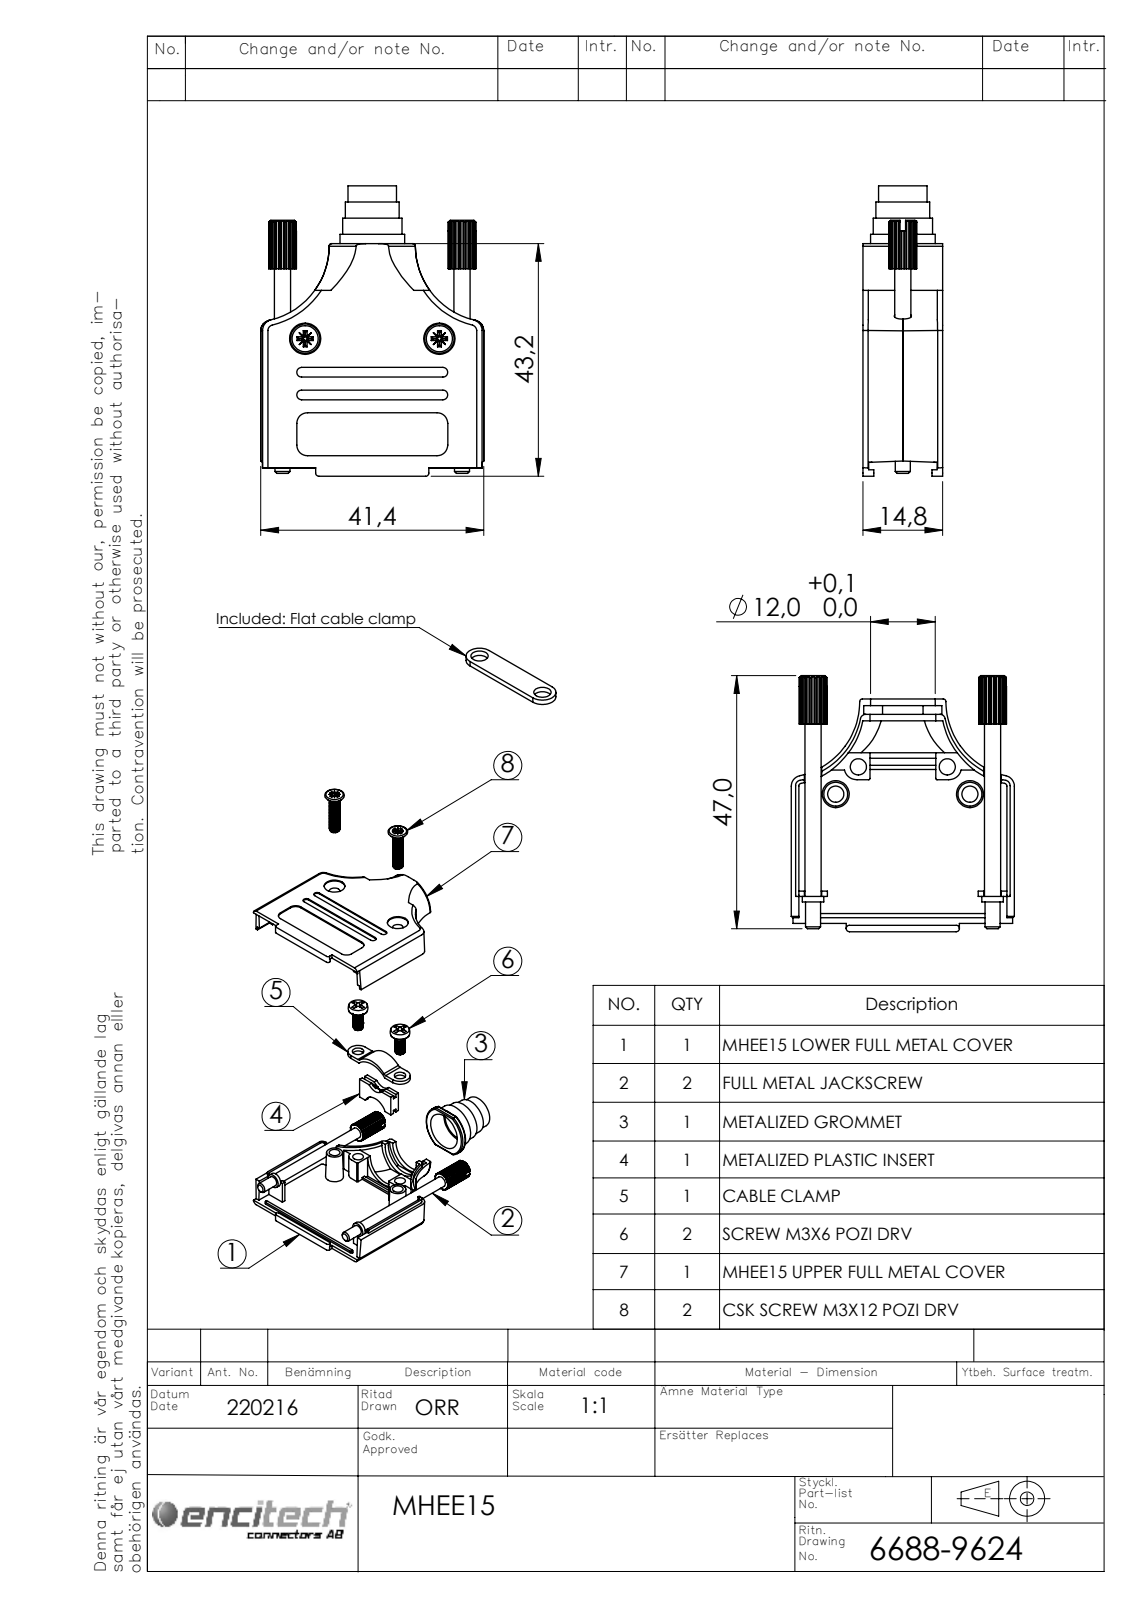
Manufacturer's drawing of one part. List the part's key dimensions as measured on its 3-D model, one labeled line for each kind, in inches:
Part name (STEP PRODUCT): 6560-0137-02; 6855-0117-13; 6826-0141-02; Cone MHEE (+5 more)
STEP written by: SolidWorks 2021 (AUTOMOTIVE_DESIGN)
Units: inches
Bodies: 11 solids, 877 faces (420 planar, 351 cylindrical, 106 other)
Overall size (bounding box): 2.122 × 1.63 × 0.583
Volume: 0.411 in³ · Surface area: 21.14 in²
Round holes (diameter × count): ⌀0.118 ×4, ⌀0.126 ×4, ⌀0.177 ×2, ⌀0.228 ×2, ⌀0.295 ×1, ⌀0.335 ×1, ⌀0.374 ×1, ⌀0.413 ×1, ⌀0.472 ×1, ⌀0.48 ×1
Round bosses / shafts (diameter × count): ⌀0.114 ×4, ⌀0.209 ×2, ⌀0.157 ×2, ⌀0.118 ×2, ⌀0.11 ×2, ⌀0.433 ×1, ⌀0.394 ×1, ⌀0.354 ×1
Partial cylindrical surfaces — rounded edges, fillets, slot ends (radius × count): R0.039 ×14, R0.557 ×12, R0.004 ×8, R0.008 ×4, R0.012 ×4, R0.035 ×4, R0.079 ×4, R0.01 ×3
Main face-to-face distances: 0.541, 0.041, 0.5, 0.583, 0.03, 0.571, 0.53, 0.25, 0.291, 0.28
Hole centre spacings: 0.259, 0.656, 0.839, 0.65, 0.98, 1.311
